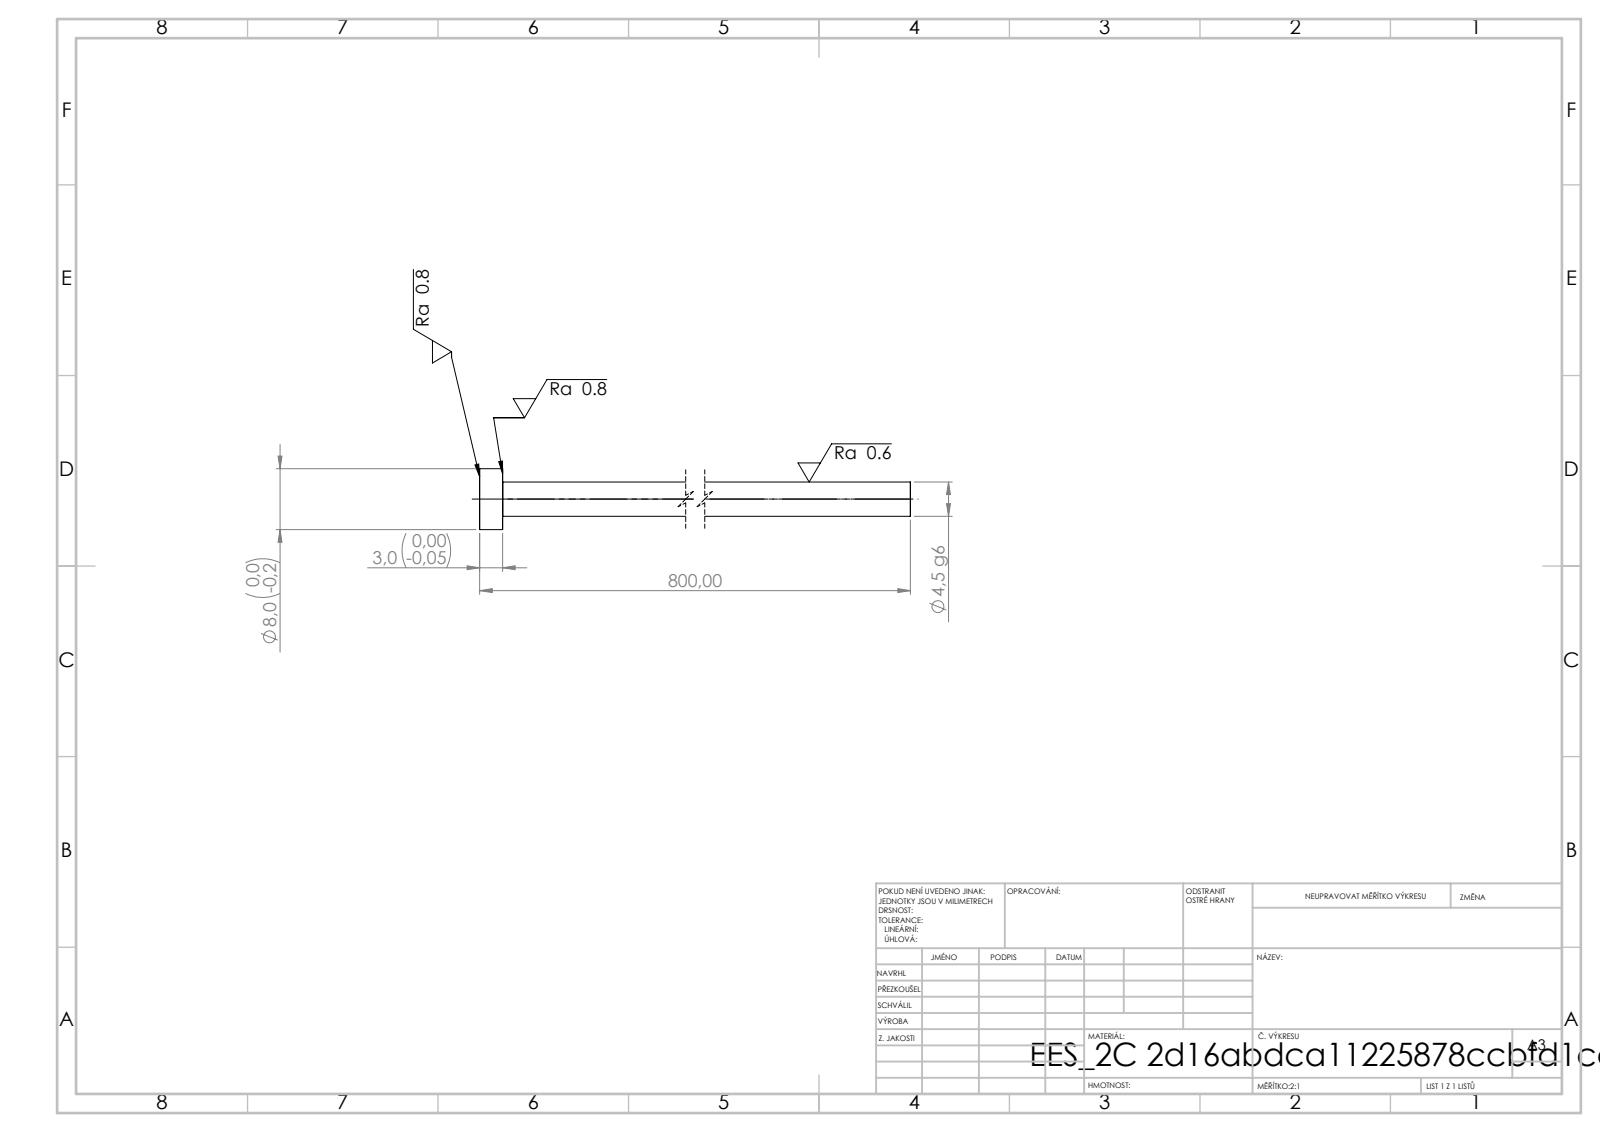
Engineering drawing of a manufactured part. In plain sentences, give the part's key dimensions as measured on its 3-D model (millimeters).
Its 3-D file was written by "SolidWorks 2019 (CONFIG_CONTROL_DESIGN)". It is 1 solid with 7 faces: 3 planar, 4 cylindrical and 0 other. Overall it measures 800 by 8 by 8 millimeters. Its volume is 12 827 cubic millimeters and its surface area 11 443 square millimeters. Round bosses or shafts: 1 of diameter 8, 1 of diameter 4.5. The main face-to-face distances are 3, 800, 797.
